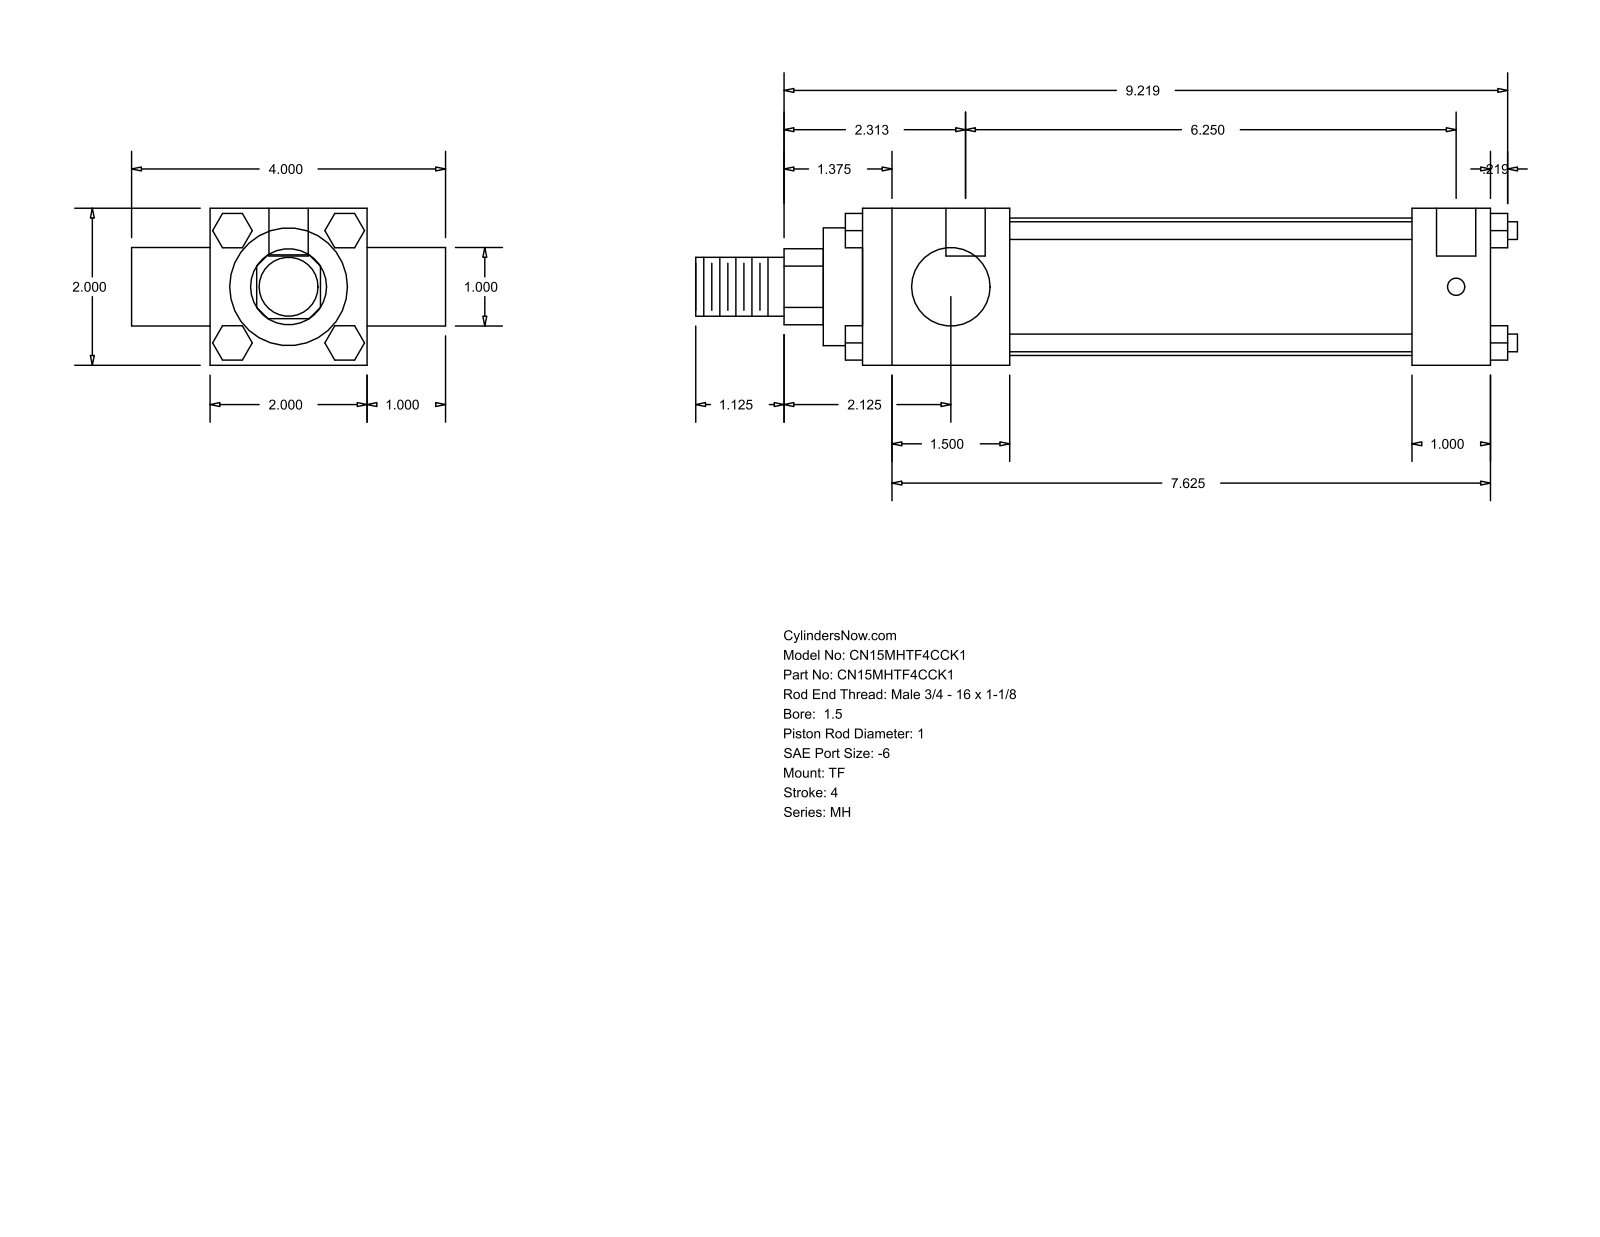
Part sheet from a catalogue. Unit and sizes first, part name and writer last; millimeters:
Units: millimetres
Overall size (bounding box): 265.91 × 101.6 × 50.8
Round holes (diameter × count): ⌀5.56 ×3, ⌀12.7 ×2
Round bosses / shafts (diameter × count): ⌀5.71 ×4, ⌀25.4 ×2, ⌀44.45 ×1, ⌀38.1 ×1, ⌀19.05 ×1
Partial cylindrical surfaces — rounded edges, fillets, slot ends (radius × count): R12.29 ×1
Main face-to-face distances: 50.8, 25.4, 203.2, 76.2, 47.63, 155.57, 177.8, 130.17, 101.6, 12.7
Hole centre spacings: 3.18, 158.75, 161.93
Bodies: 0 solids, 120 faces (92 planar, 28 cylindrical, 0 other)
Part name (STEP PRODUCT): MH_TF__0150_1
STEP written by: GSSL Pune (CONFIG_CONTROL_DESIGN)
